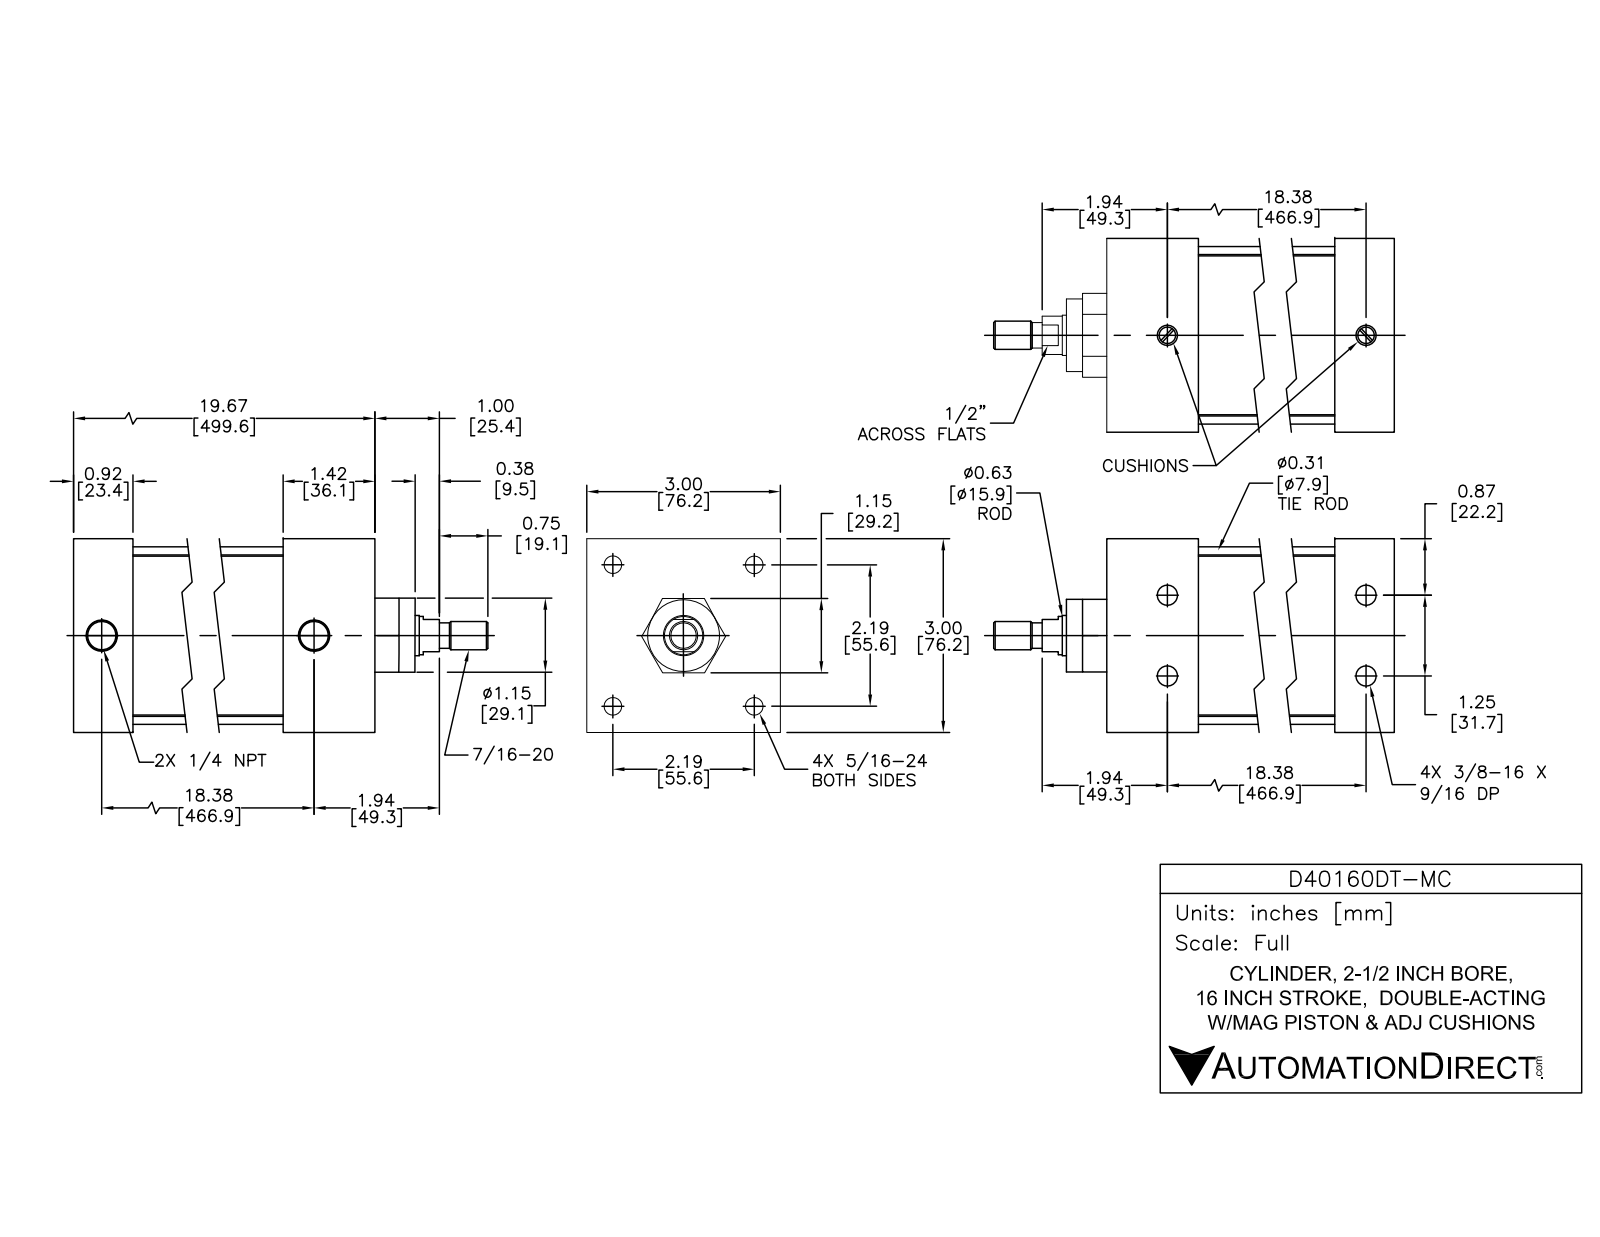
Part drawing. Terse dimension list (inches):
name: D40160DT-M PISTON; D40160DT-M BODY; D40160DT-MC
written by: SolidWorks 2015 (AUTOMOTIVE_DESIGN)
unit: in
bodies: 12 solids, 298 faces (94 planar, 114 cylindrical, 90 other)
size: 21.496 × 3 × 3
volume: 54.56 in³; area: 504.5 in²
holes: 4× ⌀0.267, 4× ⌀0.307, 4× ⌀0.359, 4× ⌀0.5, 2× ⌀0.297, 2× ⌀0.477, 1× ⌀0.625, 1× ⌀0.628, 1× ⌀2.5
bosses: 4× ⌀0.484, 4× ⌀0.313, 4× ⌀0.282, 1× ⌀2.75, 1× ⌀2.497, 1× ⌀1.12, 1× ⌀0.622, 1× ⌀0.59
rounds: 4× R0.3
face distances: 3, 19.746, 18.726, 1.02, 1.42, 17.306, 18.326, 1, 18.826, 17.406
hole spacings: 1.556, 2.2, 18.381, 18.37, 0.625, 0.625, 1.25, 3.111
